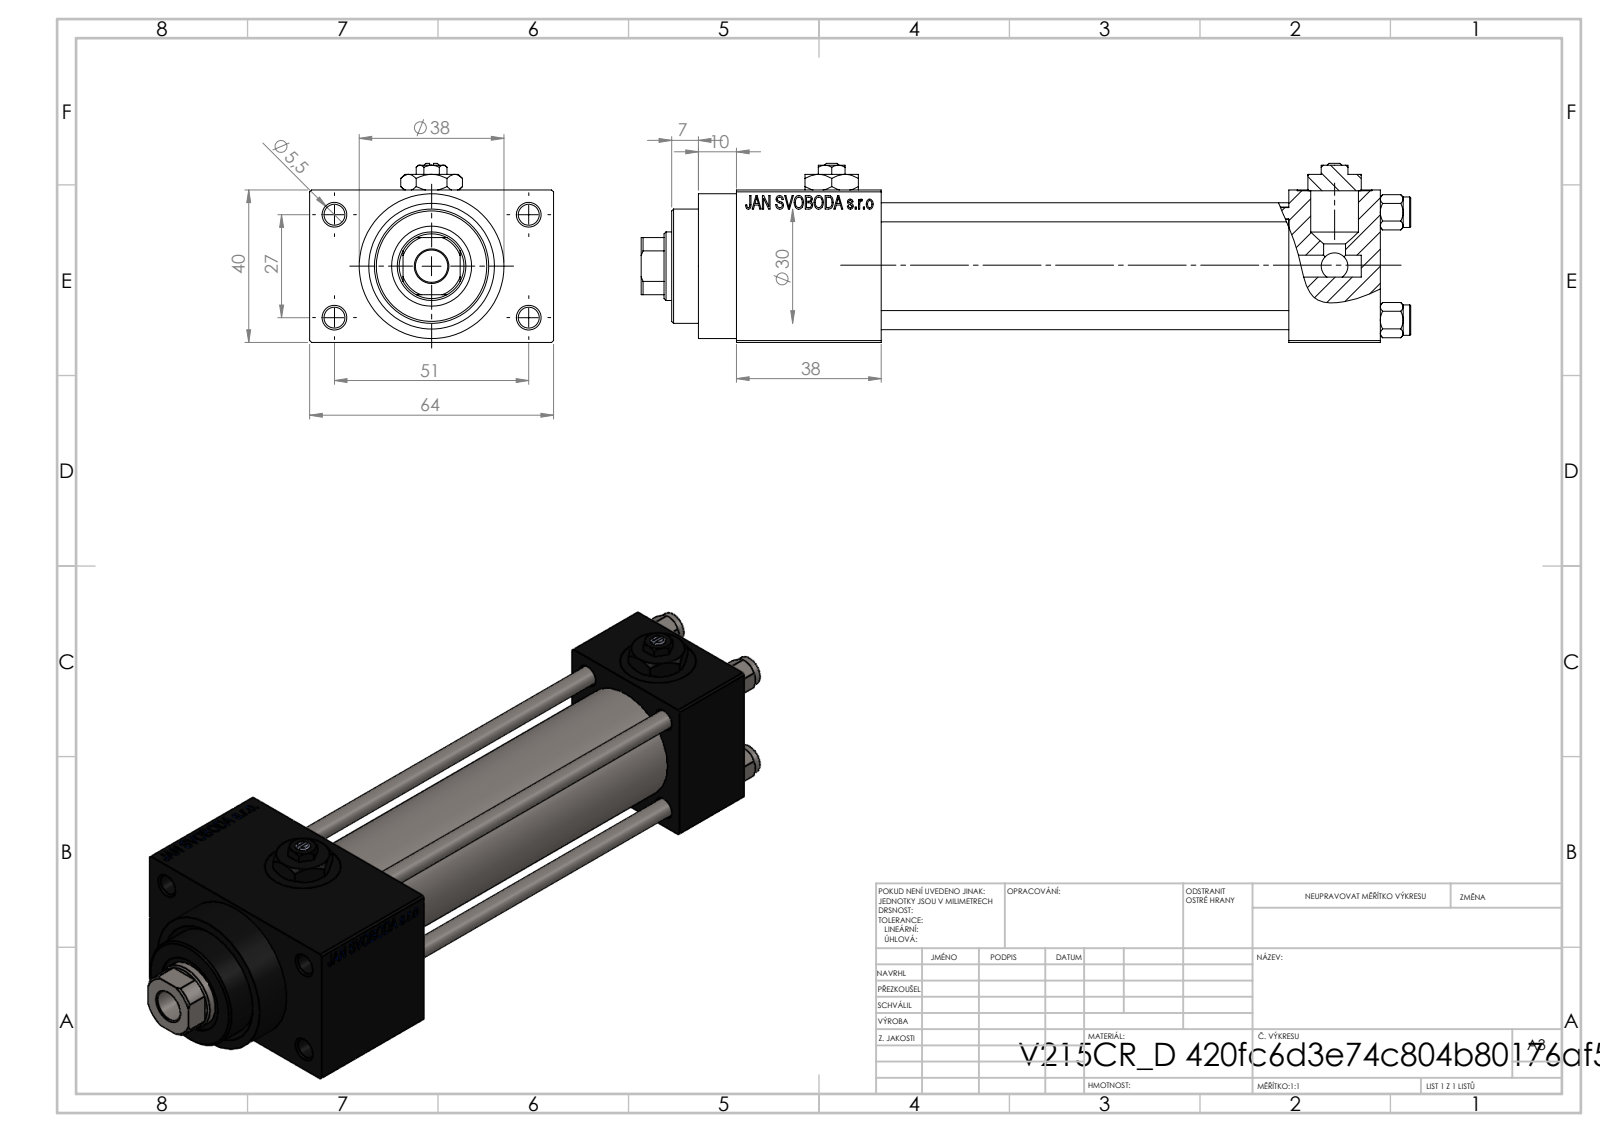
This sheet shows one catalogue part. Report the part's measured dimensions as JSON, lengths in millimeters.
{"part_name": "Zatka_pro_OIL_PORT; NUT_M5_D; V215CR_D_Body; V215CR_D_TYCINKA (+2 more)", "step_written_by": "SolidWorks 2019 (CONFIG_CONTROL_DESIGN)", "units": "millimeters", "bodies": {"solids": 13, "faces": 1200, "planar": 541, "cylindrical": 97, "other": 562}, "overall_size": [202, 64, 47], "volume_mm3": 213912, "surface_area_mm2": 83994, "round_holes": [[20, 5], [5, 4], [5.5, 4], [13.16, 4], [7, 3], [8.5, 1], [18, 1], [21, 1], [25, 1], [30, 1]], "round_bosses_or_shafts": [[8, 4], [38, 1], [31, 1]], "partial_cylinders_radius": [[8.5, 1]], "face_to_face_distances": [40, 12, 107, 52, 24, 131, 38, 145, 169, 64], "hole_center_spacings": [11.37, 20.01, 28.3, 28.85, 29.89, 39.66, 48.34, 27]}
